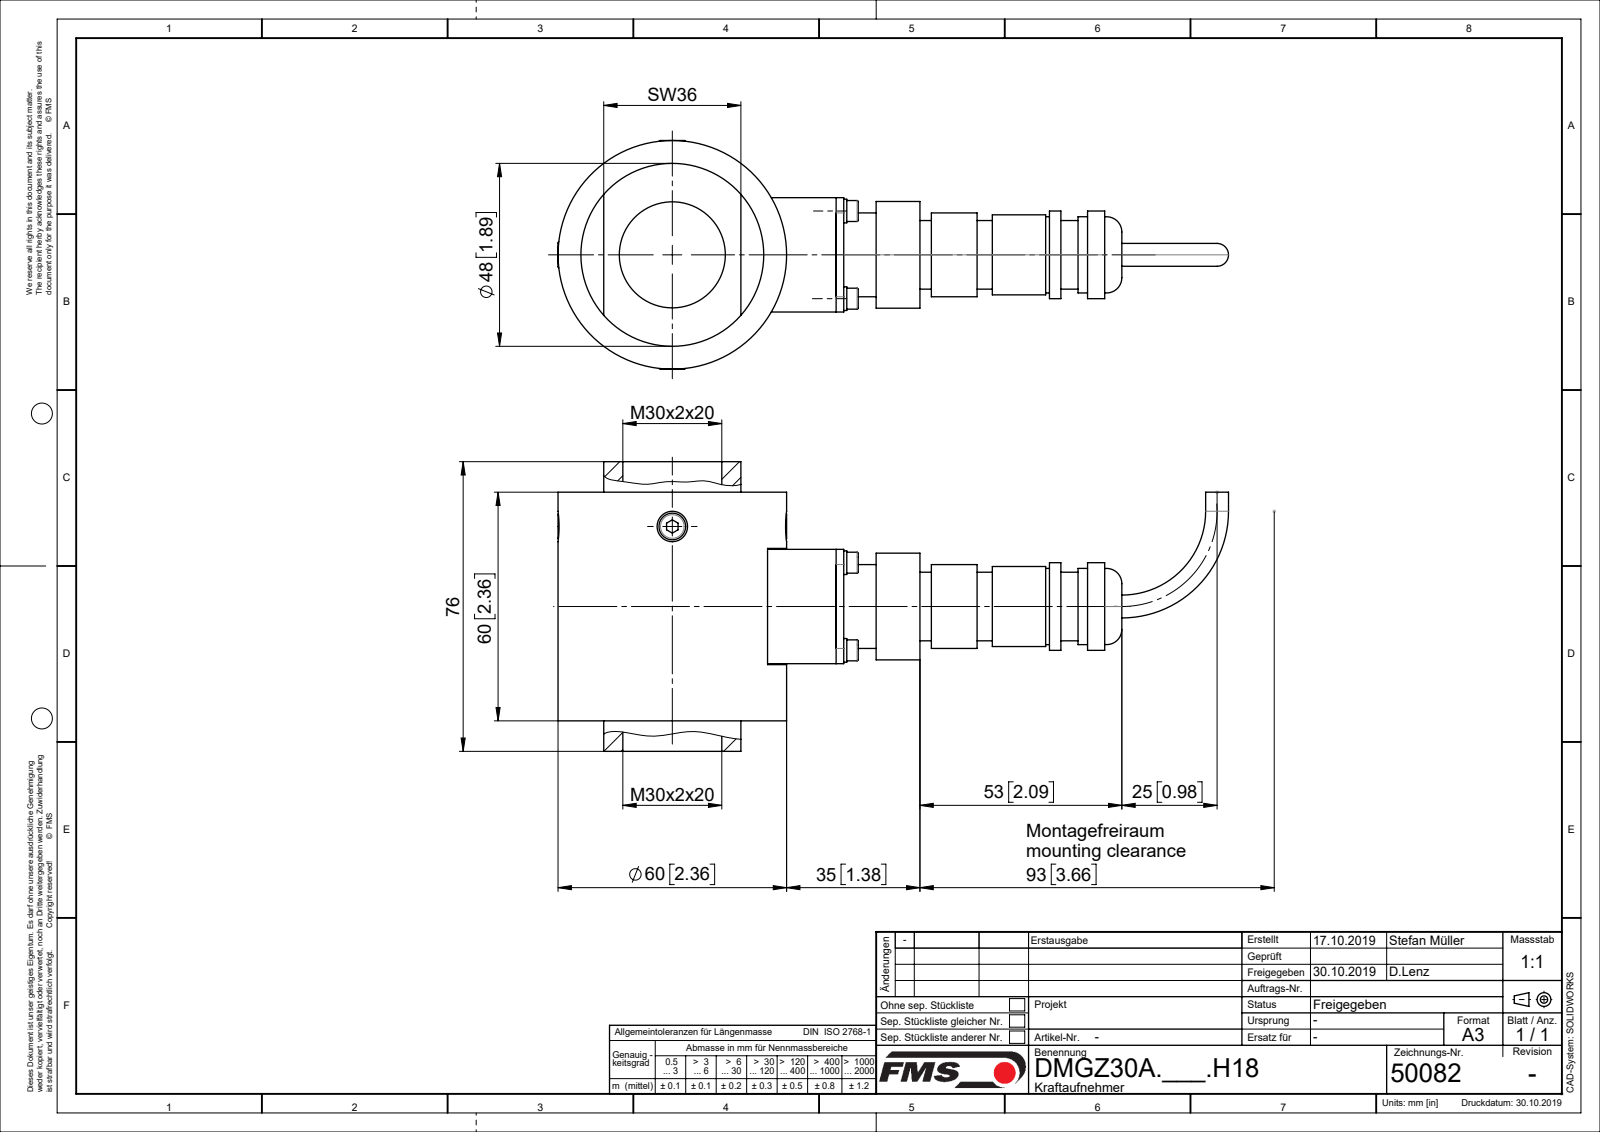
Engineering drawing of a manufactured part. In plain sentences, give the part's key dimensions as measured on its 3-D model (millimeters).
The part is named "D50082; D4948204; TEIL1; D49483 (+6 more)". Its 3-D file was written by "Mechanical Desktop 2007 (CONFIG_CONTROL_DESIGN)". It is 16 solids with 283 faces: 83 planar, 152 cylindrical and 48 other. Overall it measures 176 by 88 by 60 millimeters. Its volume is 205 342 cubic millimeters and its surface area 59 130 square millimeters. Round holes: 4 of diameter 2.6, 4 of diameter 3.2, 4 of diameter 3.4, 2 of diameter 3.42, 2 of diameter 4.3, 2 of diameter 8, 1 of diameter 23, 1 of diameter 28.21, 1 of diameter 30.5, 1 of diameter 48. Round bosses or shafts: 4 of diameter 6.2, 4 of diameter 5.5, 4 of diameter 3, 4 of diameter 2.5, 2 of diameter 7, 2 of diameter 4, 1 of diameter 60, 1 of diameter 28. Partial cylindrical surfaces (rounded edges, fillets, slot ends): 4 of radius 4. The main face-to-face distances are 20, 8, 68, 56, 3, 15, 12, 18, 23, 43. The hole center spacings are 16.26, 23, 14.92, 32.53, 34.47, 21.
